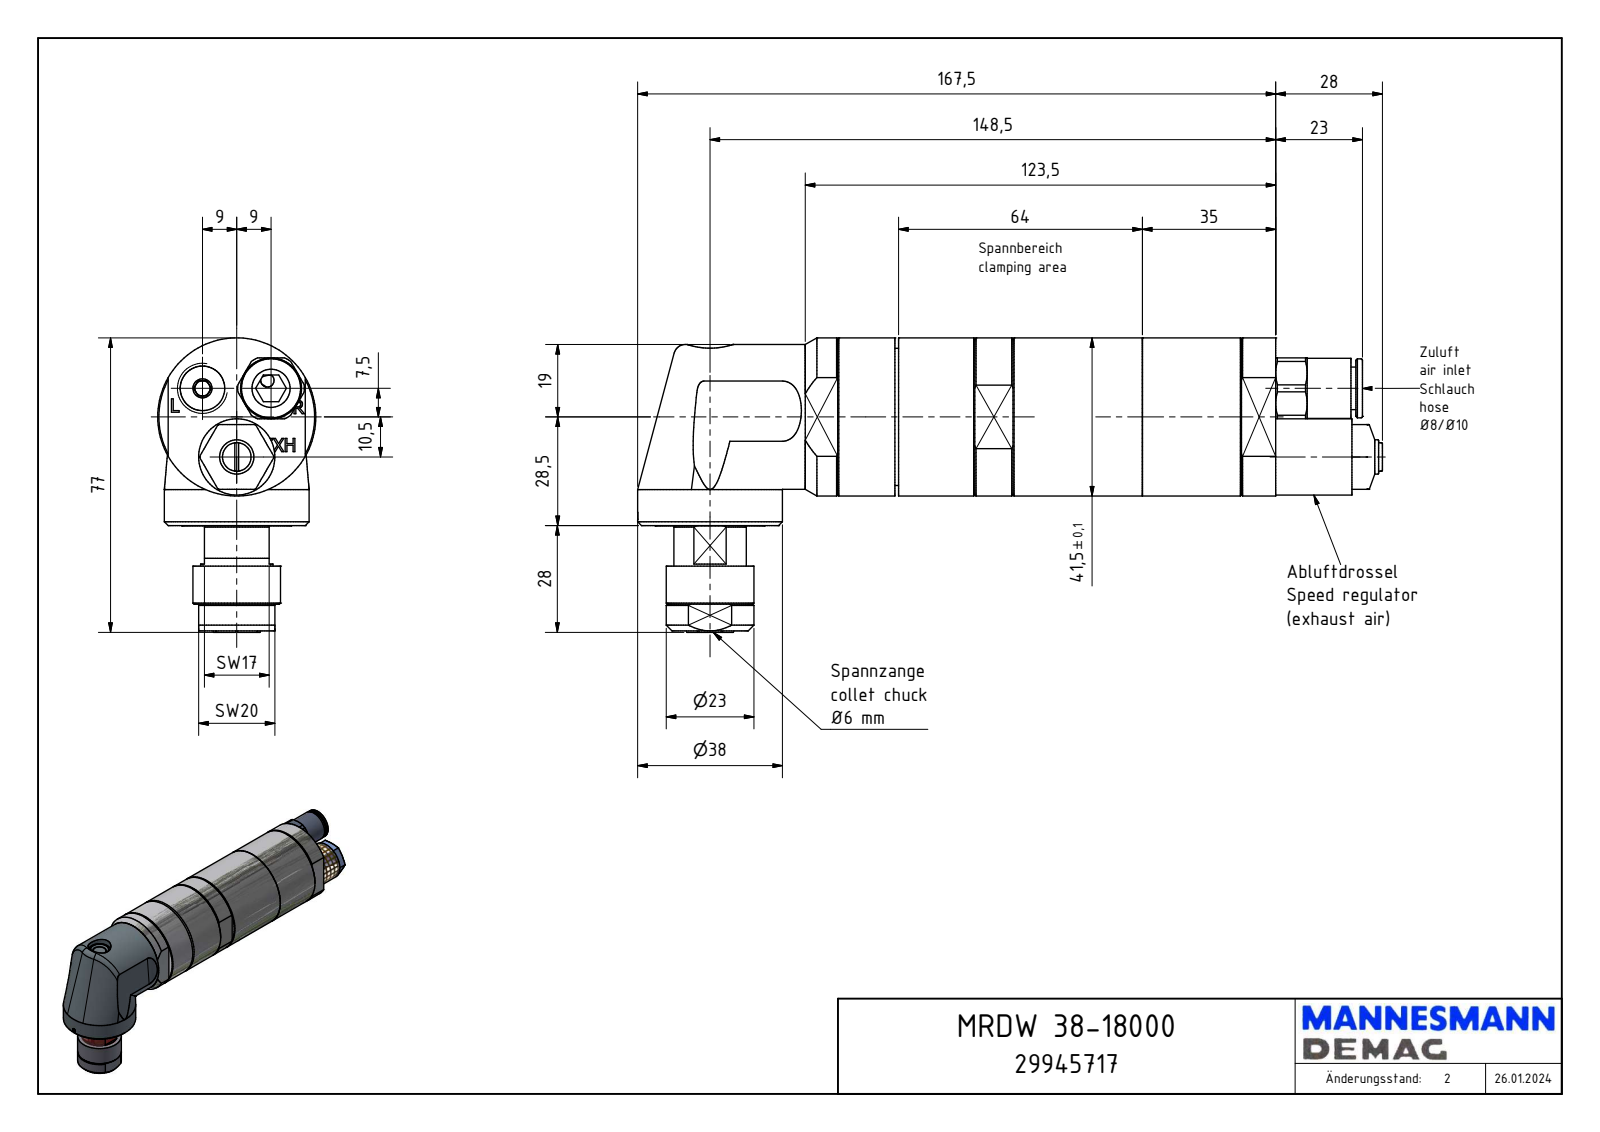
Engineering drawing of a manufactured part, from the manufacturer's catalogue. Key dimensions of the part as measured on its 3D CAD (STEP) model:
Part name (STEP PRODUCT): MRDW 38-18000_29945717
STEP written by: Autodesk Inventor 2024 (AUTOMOTIVE_DESIGN)
Units: millimetres
Bodies: 3 solids, 402 faces (216 planar, 72 cylindrical, 114 other)
Overall size (bounding box): 195.5 × 77.27 × 41.5
Volume: 236 913 mm³ · Surface area: 35 759 mm²
Round holes (diameter × count): ⌀3 ×2, ⌀2 ×1, ⌀6 ×1, ⌀8.5 ×1, ⌀10 ×1, ⌀10.5 ×1, ⌀11.45 ×1, ⌀12 ×1, ⌀13.2 ×1, ⌀17.92 ×1, ⌀19 ×1, ⌀19.2 ×1
Round bosses / shafts (diameter × count): ⌀38 ×2, ⌀41.5 ×1, ⌀23 ×1, ⌀20 ×1, ⌀15.75 ×1, ⌀15.5 ×1, ⌀14 ×1, ⌀11.2 ×1
Partial cylindrical surfaces — rounded edges, fillets, slot ends (radius × count): R18.09 ×6, R33.72 ×6, R8 ×2, R8.75 ×1, R16.5 ×1
Main face-to-face distances: 0.5, 1, 18.25, 36, 17.75, 37, 17, 18.75, 19.25, 28
Hole centre spacings: 12.25, 24.5, 34.69
